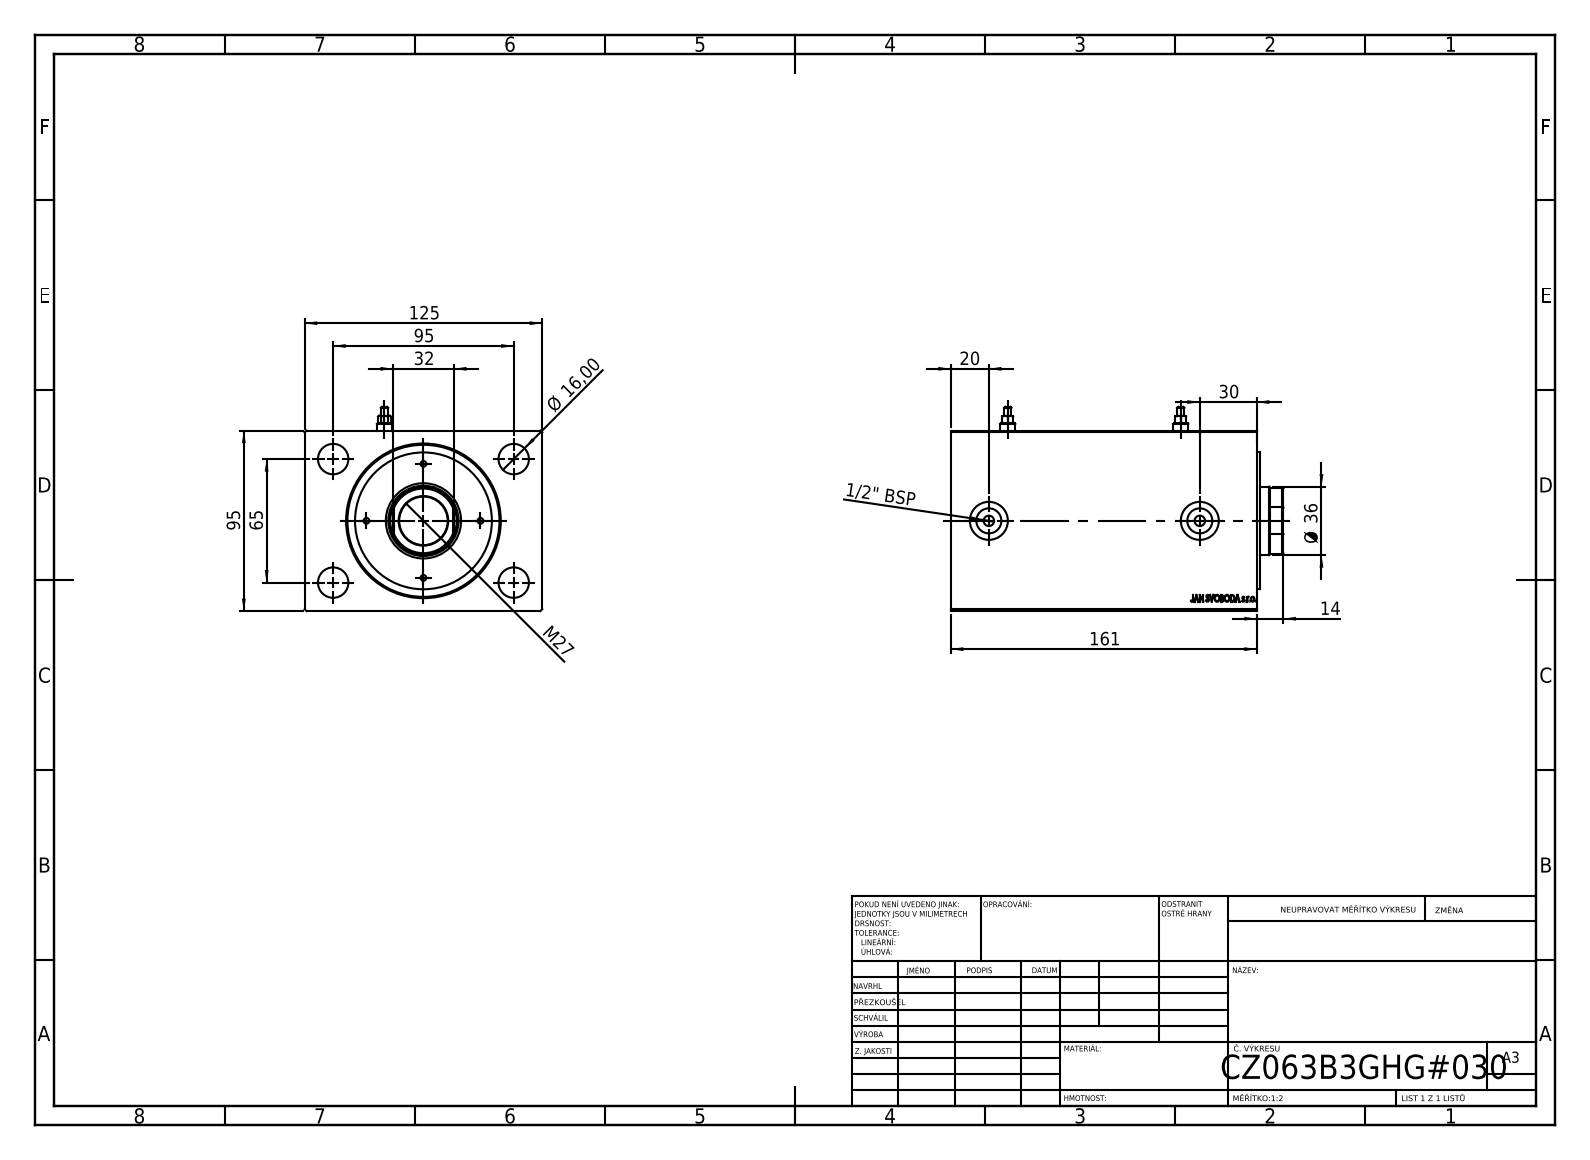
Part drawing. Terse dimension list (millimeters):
name: Zatka_Cushioning3; V500CZ_B_VC; V500CZ
written by: SolidWorks 2019 (CONFIG_CONTROL_DESIGN)
unit: mm
bodies: 5 solids, 934 faces (424 planar, 74 cylindrical, 436 other)
size: 175 × 125 × 107.5
volume: 1 790 000 mm³; area: 183 258 mm²
holes: 4× ⌀3, 4× ⌀16, 2× ⌀1.8, 2× ⌀5.5, 2× ⌀8, 2× ⌀13.16, 2× ⌀20, 1× ⌀25.5, 1× ⌀36, 1× ⌀37, 1× ⌀63, 1× ⌀80
bosses: 2× ⌀7.8, 2× ⌀3.8, 1× ⌀72
rounds: 1× R17.5
face distances: 95, 125, 161, 140.2, 20.8, 14, 1.8, 12.2, 128, 148.8
hole spacings: 30, 36.91, 42.43, 47.57, 57.55, 78.5, 84.04, 60
